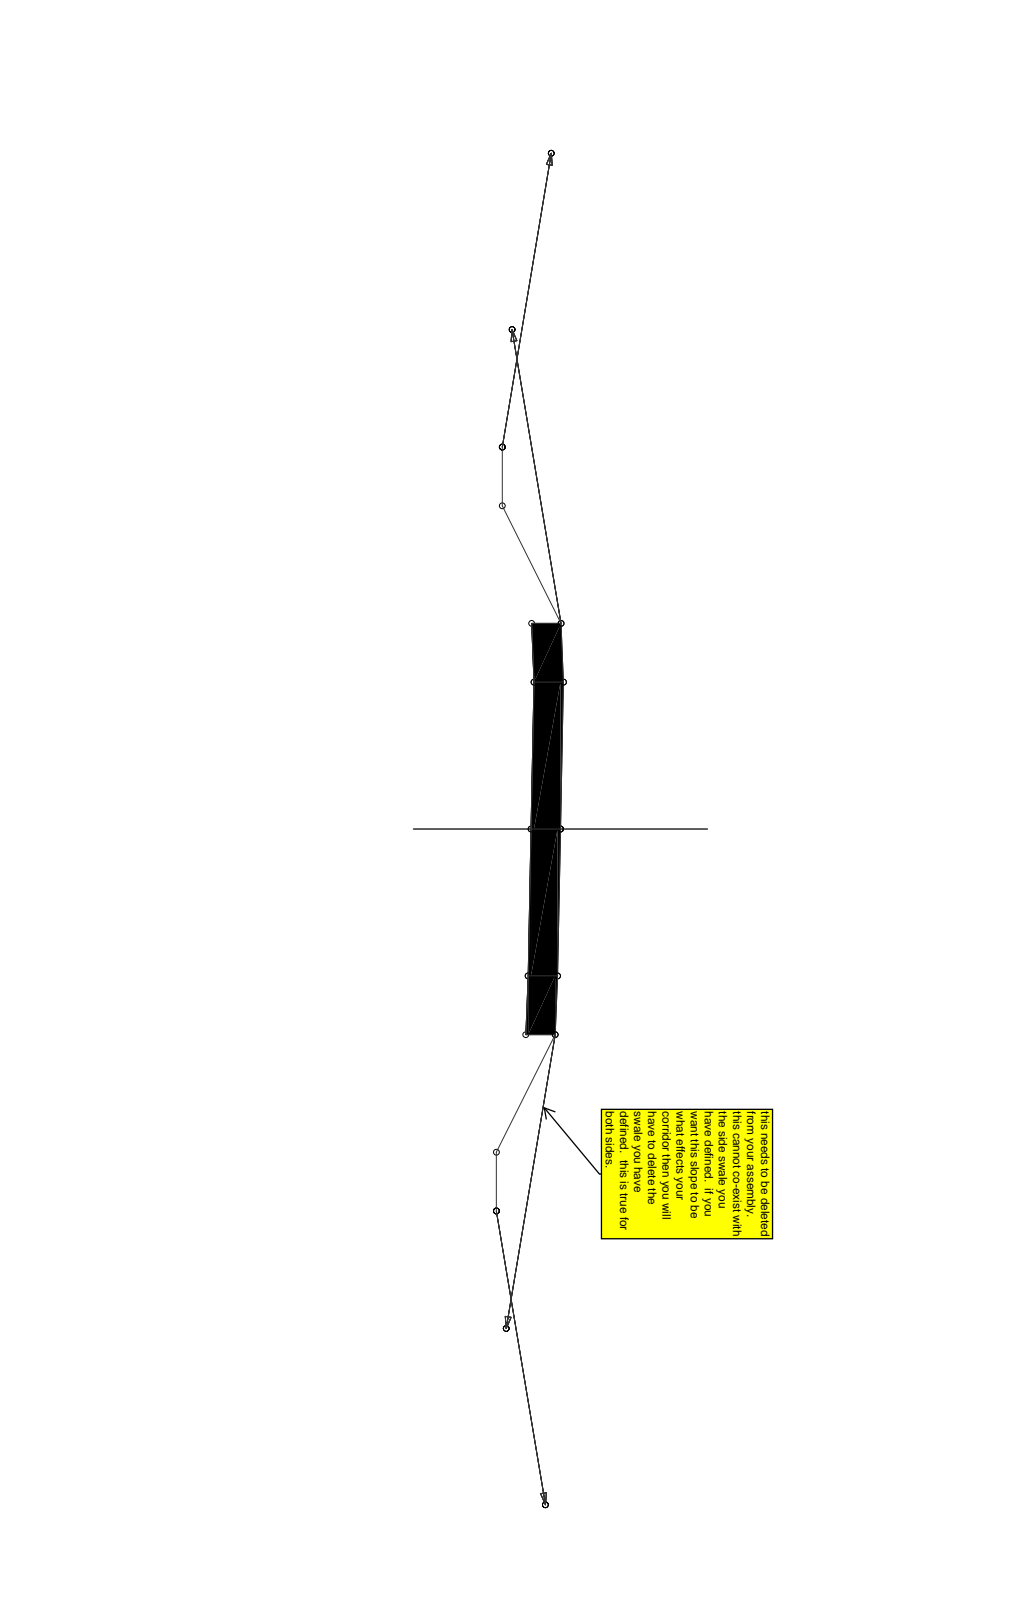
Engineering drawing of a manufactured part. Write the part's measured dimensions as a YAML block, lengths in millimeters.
part_name: "Arm^Mecanismo_Conjunto; Base^Mecanismo_Conjunto; Wheel^Mecanismo_Conjunto"
step_written_by: "SolidWorks 2014 (AUTOMOTIVE_DESIGN)"
units: millimeters
bodies: {solids: 3, faces: 54, planar: 26, cylindrical: 19, other: 9}
overall_size: [500, 200, 62]
volume: 1692000
surface_area: 294036
round_holes:
  - {diameter: 15, count: 1}
  - {diameter: 18, count: 1}
round_bosses_or_shafts:
  - {diameter: 200, count: 1}
  - {diameter: 35, count: 1}
  - {diameter: 20, count: 1}
partial_cylinders:
  - {radius: 45, count: 4}
  - {radius: 8, count: 2}
  - {radius: 10, count: 2}
  - {radius: 22, count: 2}
  - {radius: 67, count: 1}
  - {radius: 83, count: 1}
face_to_face_distances: [15, 50, 35, 40, 25, 10, 58, 43, 18, 8]
hole_center_spacings: [70]
